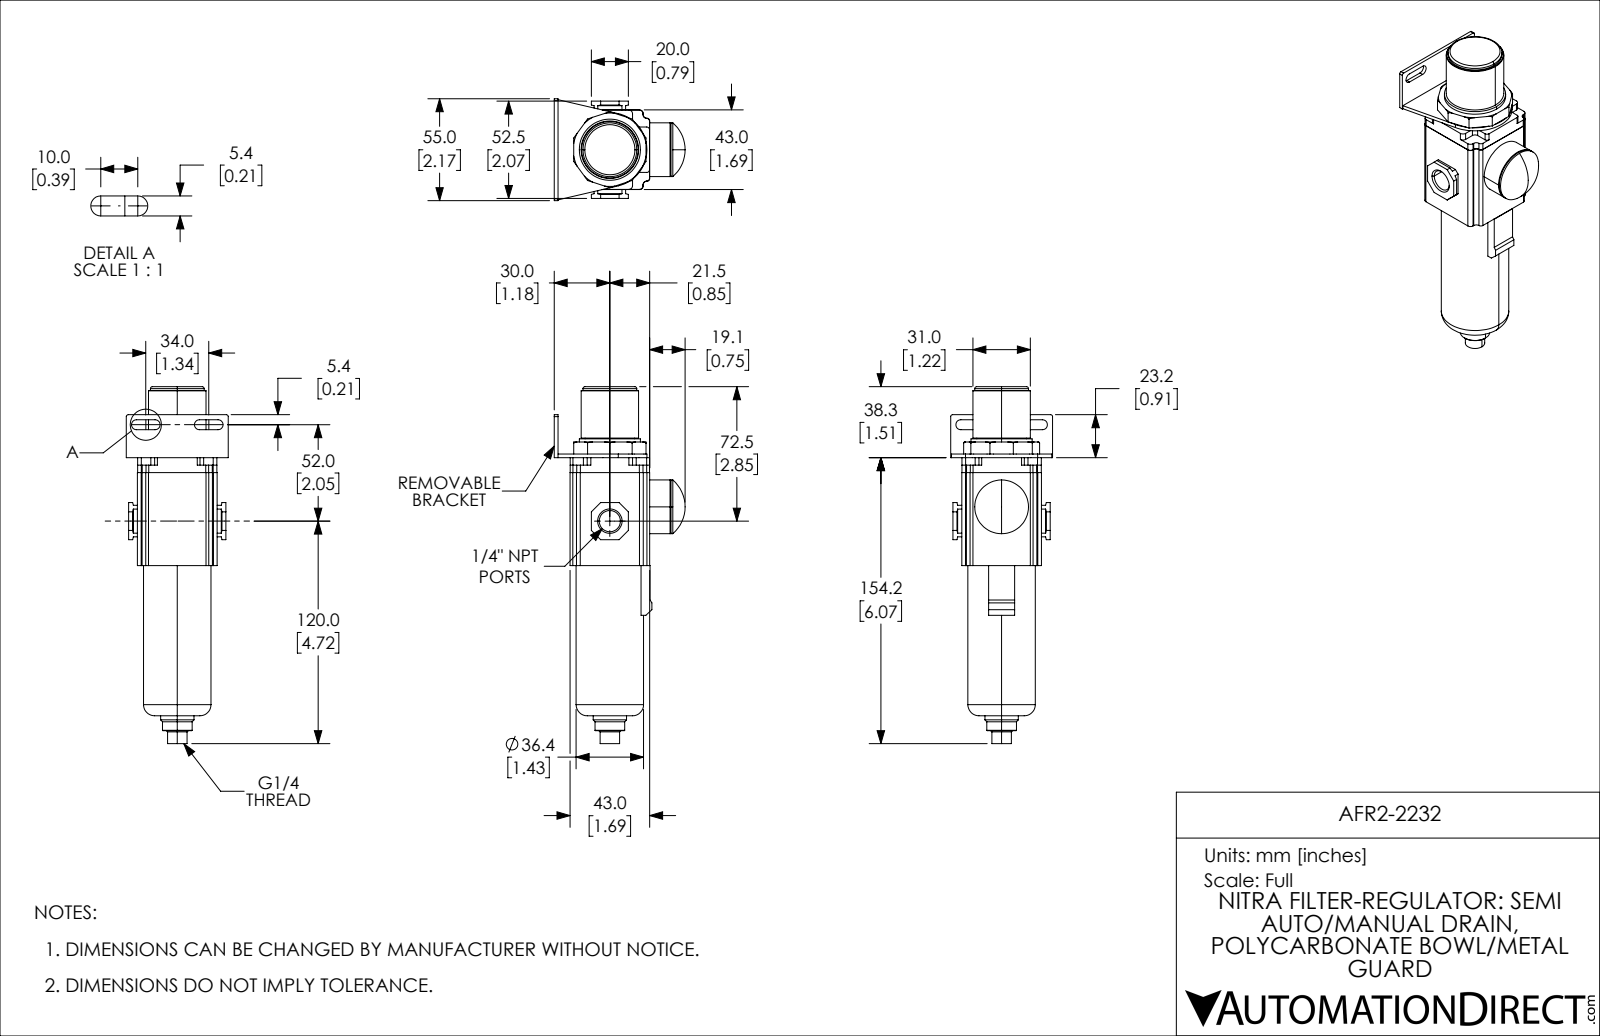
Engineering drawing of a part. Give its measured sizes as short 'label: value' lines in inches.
name: AFR2-2232
written by: SolidWorks 2019 (CONFIG_CONTROL_DESIGN)
unit: in
bodies: 1 solid, 220 faces (119 planar, 69 cylindrical, 32 other)
size: 7.579 × 2.78 × 2.165
volume: 14.48 in³; area: 52.86 in²
holes: 1× ⌀0.163, 1× ⌀0.451
bosses: 2× ⌀1.142, 1× ⌀1.433, 1× ⌀1.299, 1× ⌀1.22, 1× ⌀1.054, 1× ⌀0.709, 1× ⌀0.63, 1× ⌀0.413
rounds: 24× R0.079, 12× R0.059, 4× R0.106, 2× R0.039, 1× R0.787
face distances: 1.693, 0.079, 0.335, 0.256, 1.949, 2.028, 1.689, 1.429, 2.291, 2.37
